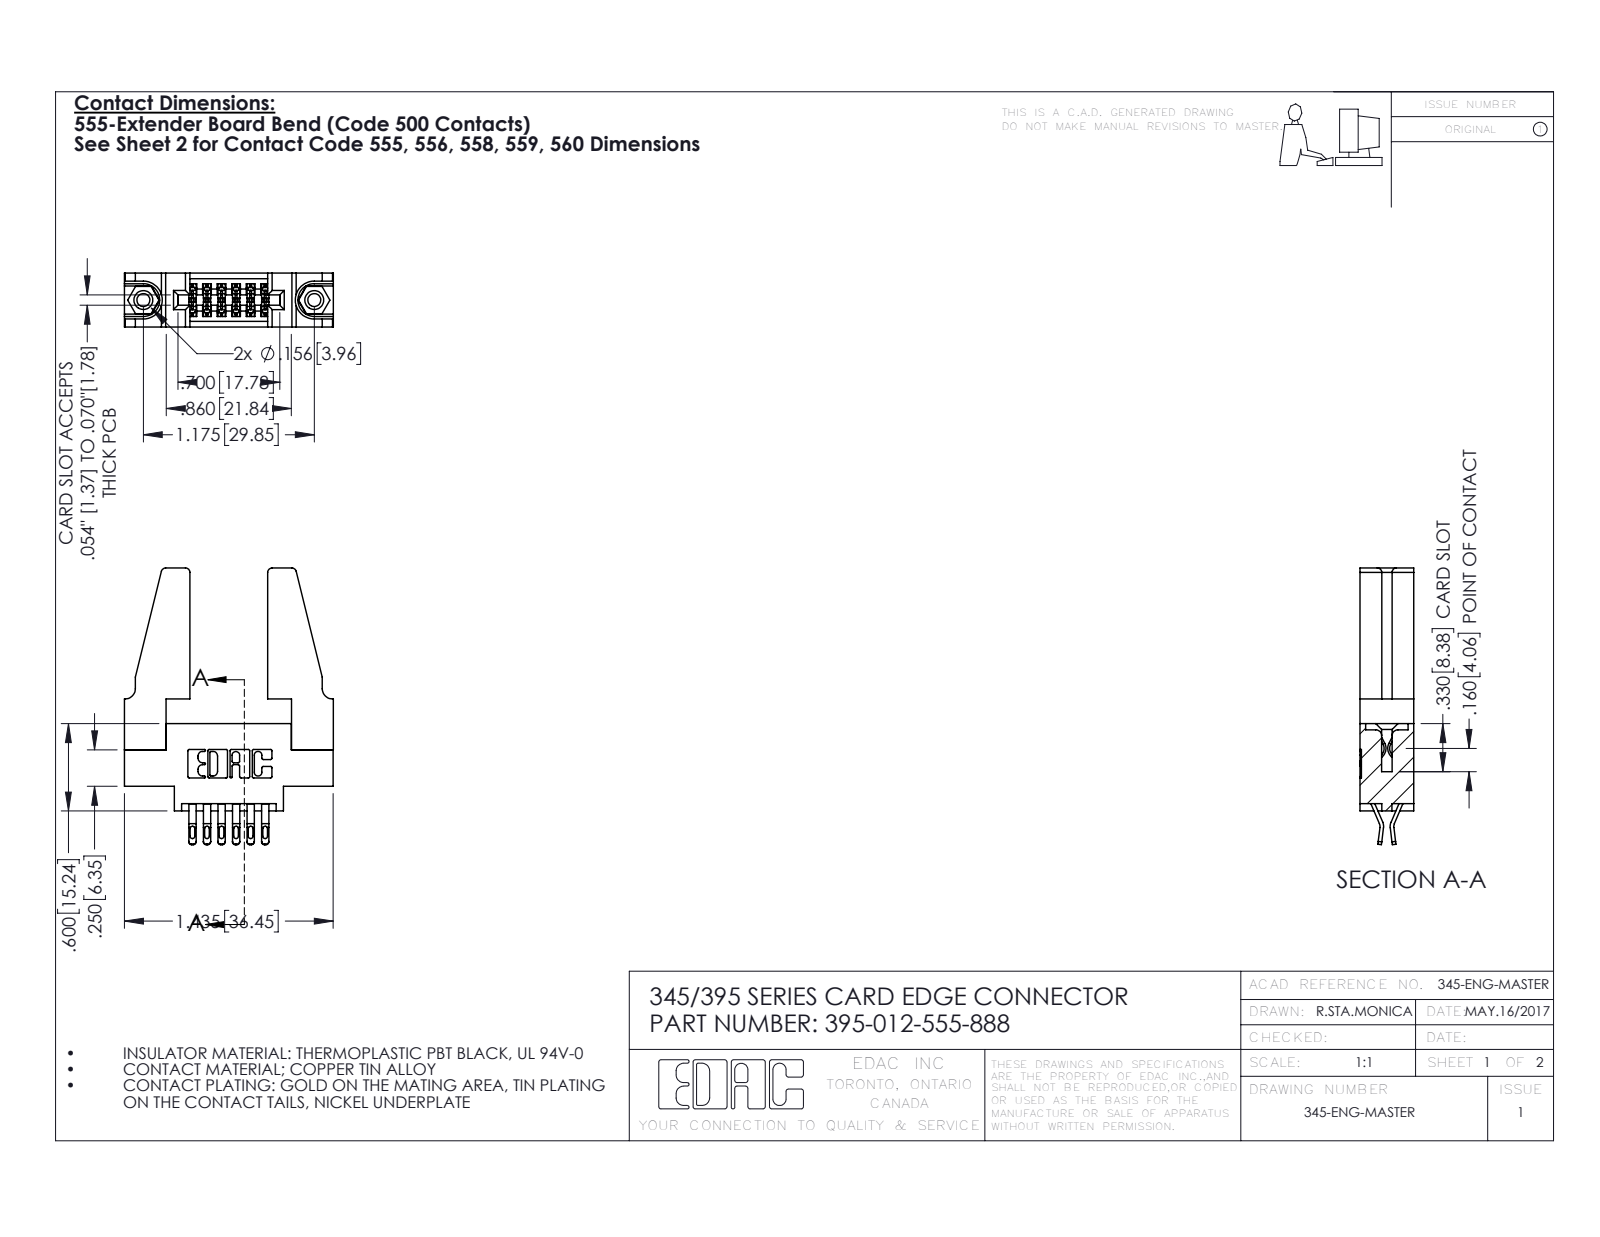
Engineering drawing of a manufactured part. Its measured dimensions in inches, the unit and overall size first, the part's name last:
Units: inches
Overall size (bounding box): 1.902 × 1.436 × 0.37
Round holes (diameter × count): ⌀0.089 ×2, ⌀0.125 ×2, ⌀0.156 ×2, ⌀0.064 ×1
Round bosses / shafts (diameter × count): ⌀0.155 ×2
Partial cylindrical surfaces — rounded edges, fillets, slot ends (radius × count): R0.016 ×30, R0.02 ×24, R0.01 ×22, R0.006 ×18, R0.03 ×8, R0.007 ×6, R0.031 ×6, R0.026 ×3
Main face-to-face distances: 0.37, 0.072, 0.298, 0.2, 0.025, 0.15, 0.148, 0.225, 0.098, 0.272
Hole centre spacings: 0.27, 0.946, 1.175
Volume: 0.39 in³ · Surface area: 11.34 in²
Bodies: 17 solids, 926 faces (528 planar, 382 cylindrical, 16 other)
Part name (STEP PRODUCT): 345 Part_0.170 Offset - 0.156 Dia-TH; 345-292-001_555 Tail; 345-220-078_345-220-088; 395-012-555-888 (+1 more)
STEP written by: SolidWorks 2016 (CONFIG_CONTROL_DESIGN)
